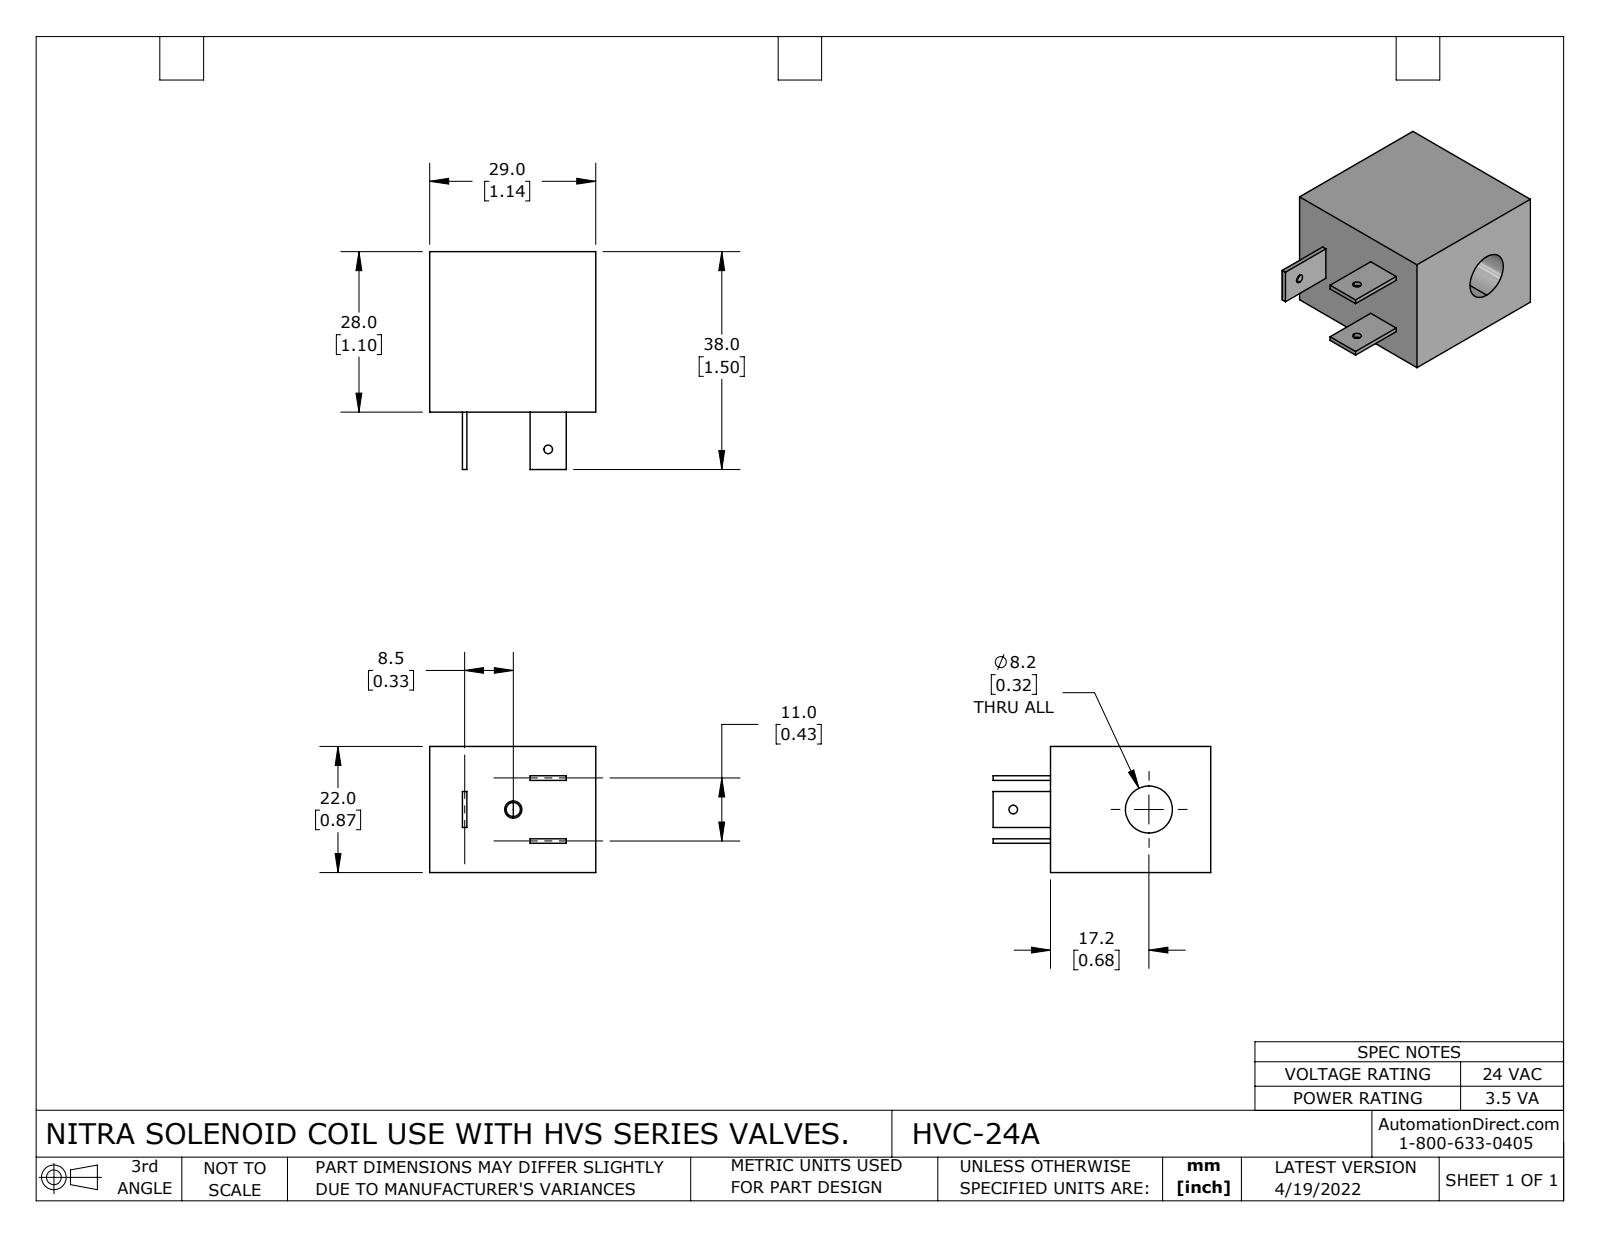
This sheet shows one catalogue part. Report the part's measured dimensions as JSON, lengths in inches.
{"part_name": "HVC-24A", "step_written_by": "SolidWorks 2021 (CONFIG_CONTROL_DESIGN)", "units": "inches", "bodies": {"solids": 1, "faces": 35, "planar": 21, "cylindrical": 10, "other": 4}, "overall_size": [1.496, 1.142, 0.866], "volume_in3": 1.004, "surface_area_in2": 8.119, "round_holes": [[0.059, 2], [0.097, 1], [0.323, 1]], "face_to_face_distances": [0.866, 1.102, 1.142, 0.031, 0.201, 0.232, 0.634, 0.665, 0.433, 0.224], "hole_center_spacings": [0.933]}
